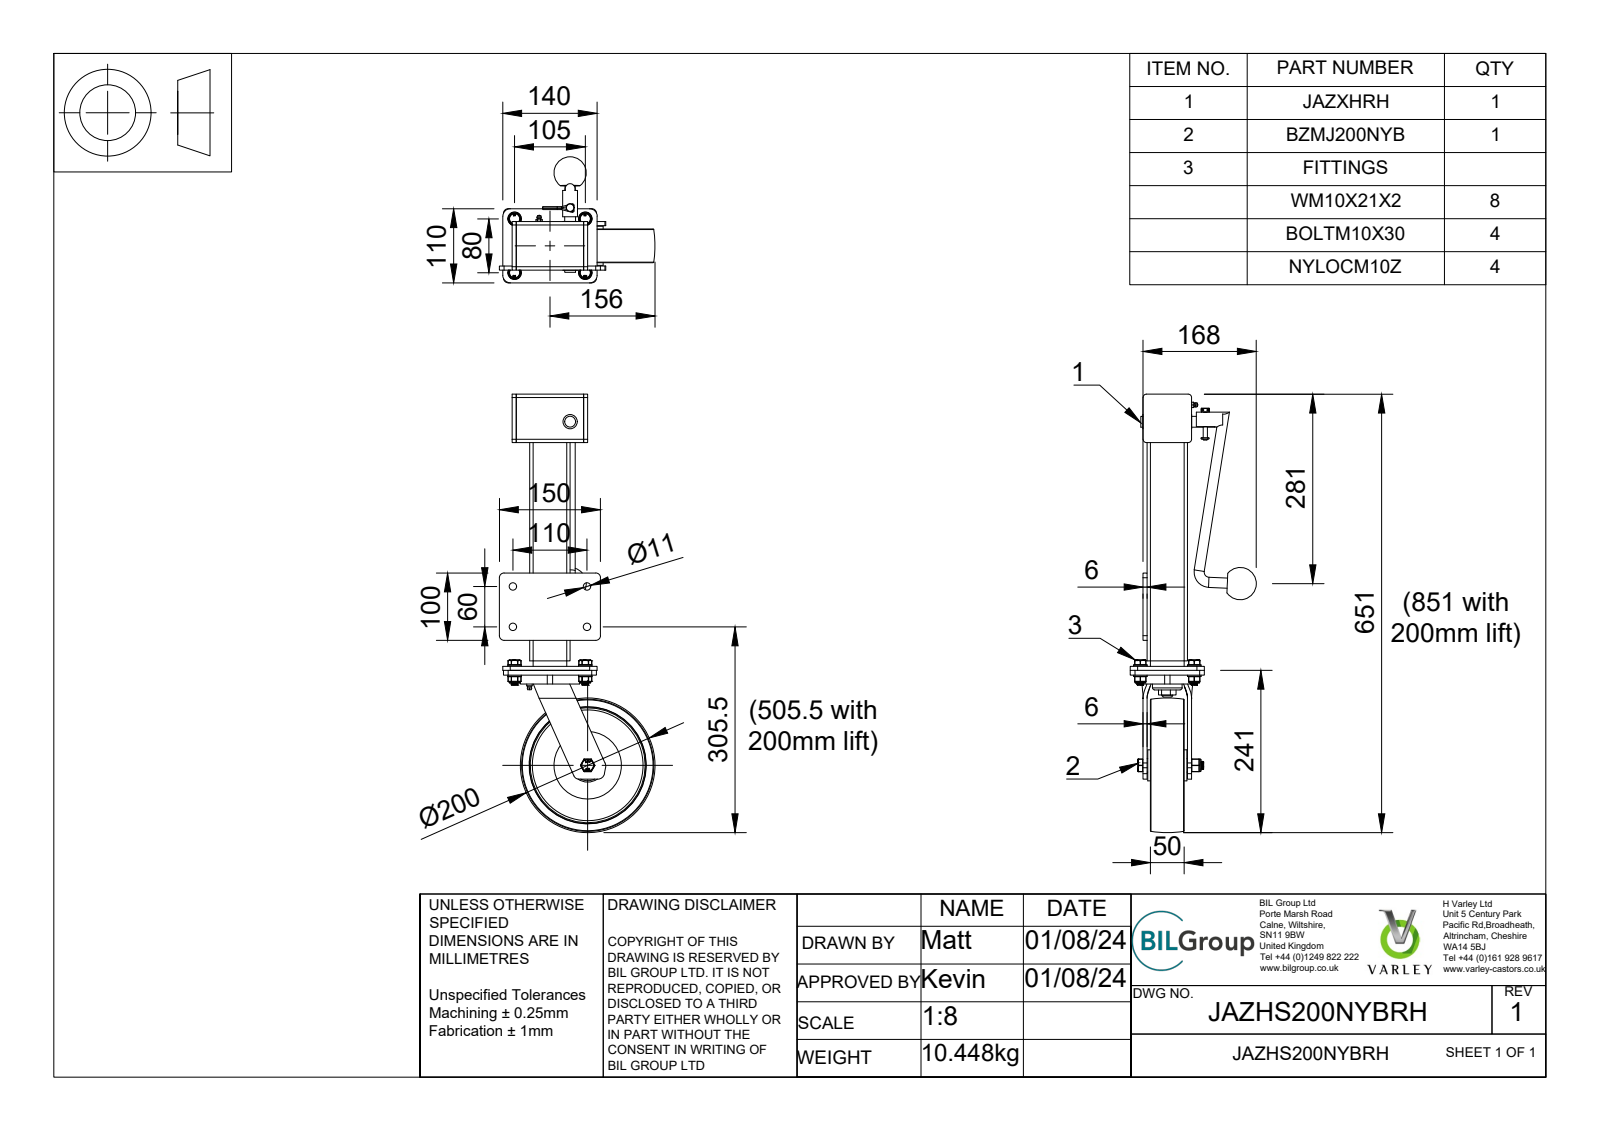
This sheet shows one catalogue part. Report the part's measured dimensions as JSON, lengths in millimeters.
{"part_name": "JAZHS200NYBRH v3; BZV200WNYRB5 v1; NYLON WHEEL; NYLON WHEEL Geometry (+7 more)", "step_written_by": "Autodesk Translation Framework v13.14.0.145 (AUTOMOTIVE_DESIGN)", "units": "millimeters", "bodies": {"solids": 52, "faces": 1440, "planar": 579, "cylindrical": 574, "other": 287}, "overall_size": [651, 231, 187.09], "volume_mm3": 2633000, "surface_area_mm2": 663547, "round_holes": [[12, 5], [10, 4], [10.5, 4], [11, 4], [16, 2], [3, 1], [6.25, 1], [6.75, 1], [12.5, 1], [13, 1], [14, 1], [15, 1]], "round_bosses_or_shafts": [[2, 10], [7.5, 8], [20, 4], [16, 4], [9.85, 4], [8.14, 4], [15, 2], [88, 1]], "partial_cylinders_radius": [[0.5, 90], [0.33, 16], [0.64, 16], [0.63, 8], [0.64, 8], [4.84, 8], [5, 8], [5.33, 8]], "face_to_face_distances": [3.5, 6, 55, 5, 1.5, 51.5, 56.5, 62.5, 50, 60], "hole_center_spacings": [66, 60, 80, 105, 110, 125.3, 132, 3.22]}
